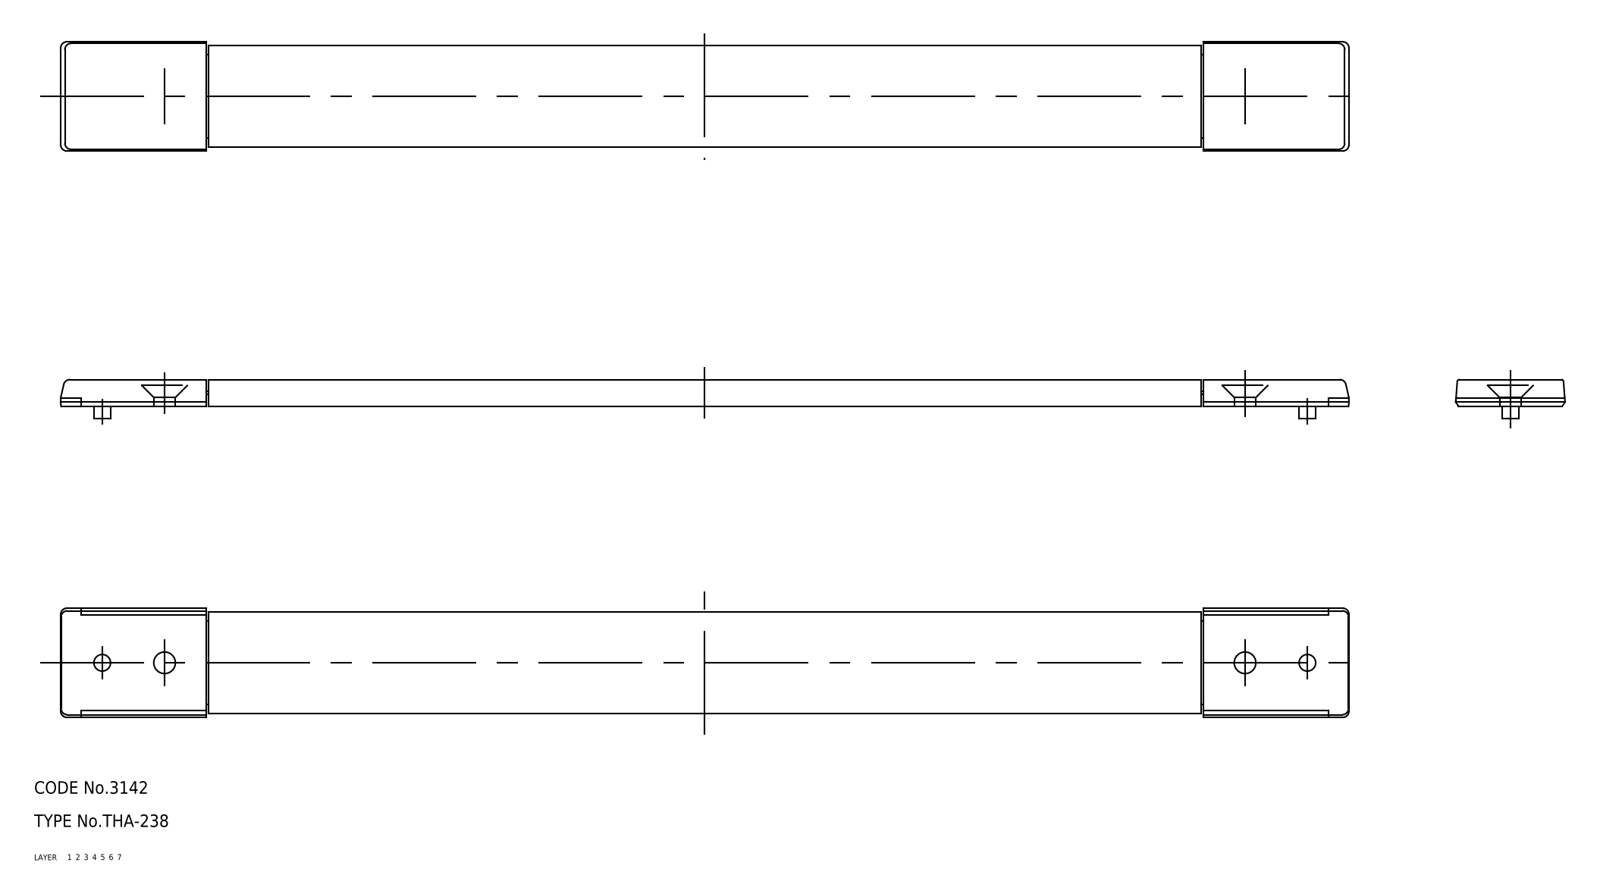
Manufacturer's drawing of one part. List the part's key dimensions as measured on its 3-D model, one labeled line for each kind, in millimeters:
Part name (STEP PRODUCT): spacer; collar; base; cover (+3 more)
STEP written by: CADfix (AUTOMOTIVE_DESIGN)
Units: millimetres
Bodies: 10 solids, 198 faces (0 planar, 0 cylindrical, 198 other)
Overall size (bounding box): 310 × 26.3 × 9.4
Volume: 37 715 mm³ · Surface area: 47 923 mm²
